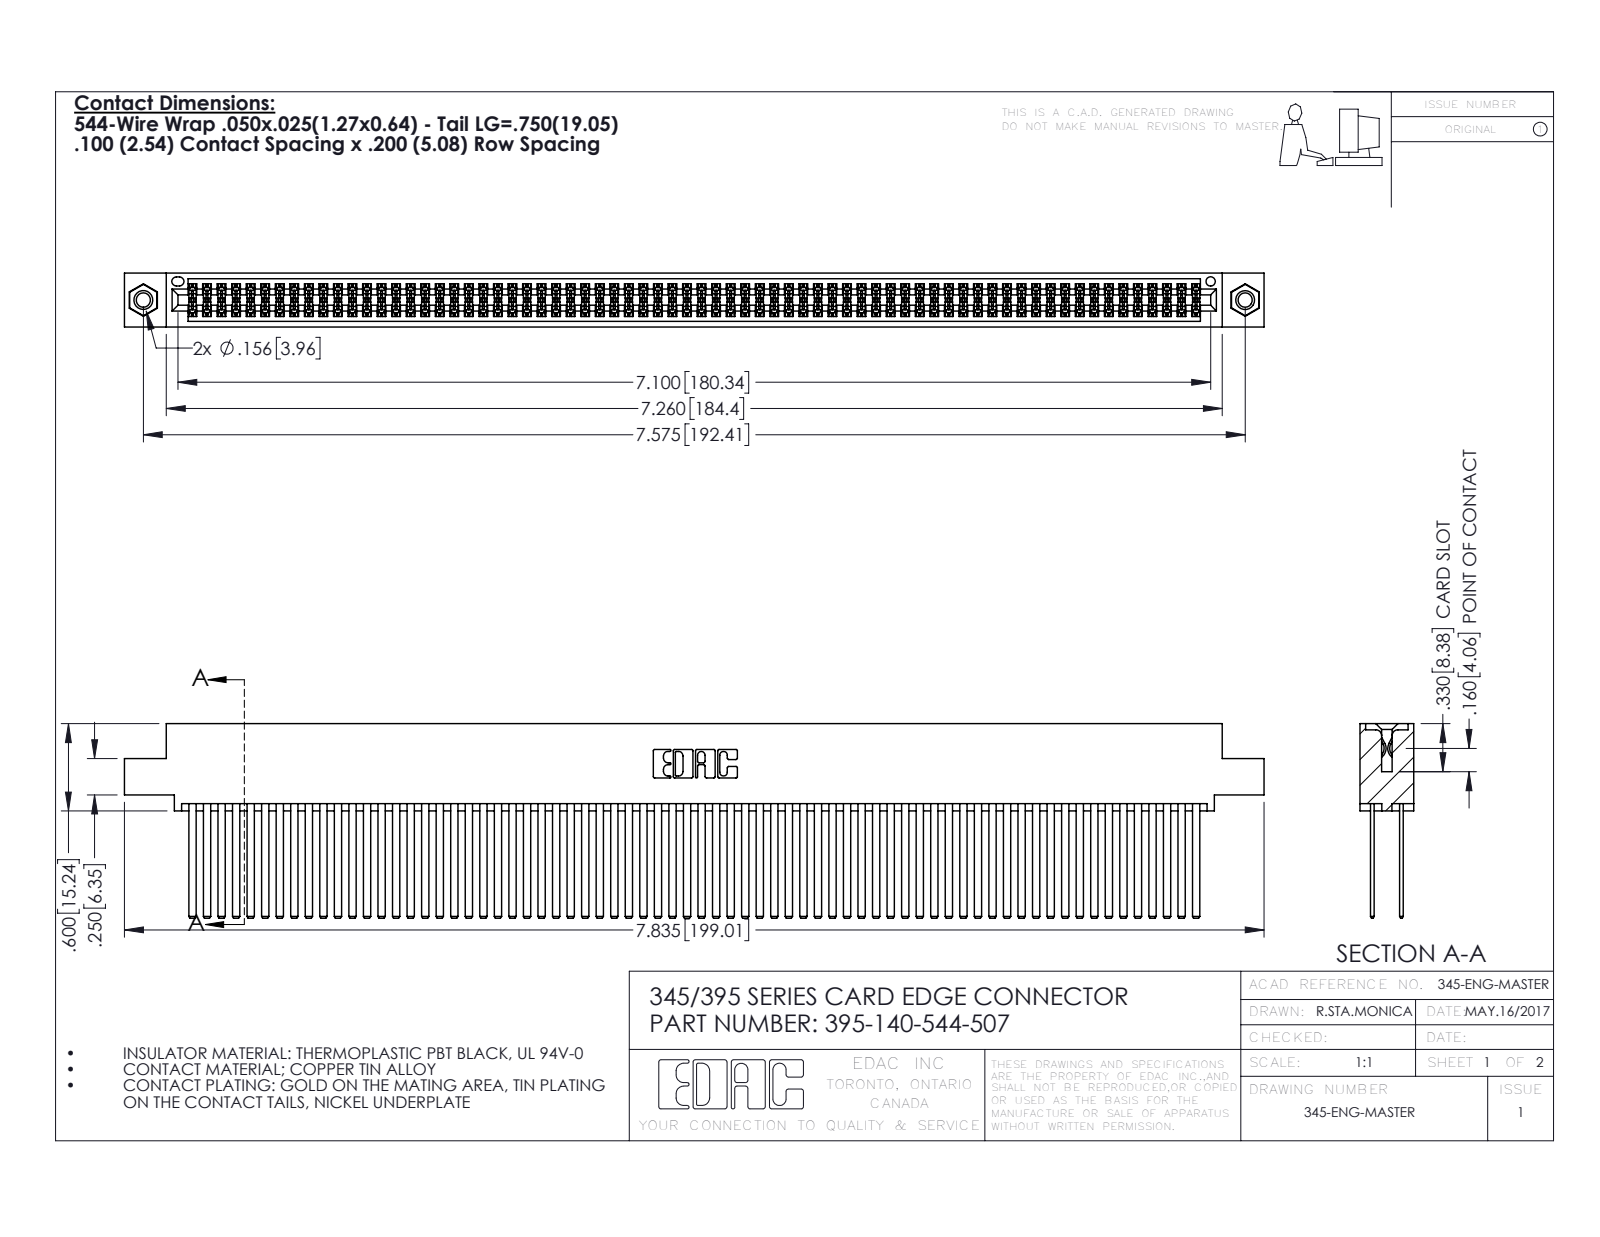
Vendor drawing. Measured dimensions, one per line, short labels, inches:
name: 345-250-001_345-250-005-103; 345 Part_0.110 Offset - 0.156 Dia-TI; 345-292-001_345-293-144; 395-140-544-507
written by: SolidWorks 2016 (CONFIG_CONTROL_DESIGN)
unit: in
bodies: 143 solids, 6350 faces (4176 planar, 2158 cylindrical, 16 other)
size: 7.835 × 1.337 × 0.37
volume: 1.31 in³; area: 59.13 in²
holes: 2× ⌀0.098, 2× ⌀0.125, 2× ⌀0.156, 1× ⌀0.064
bosses: 2× ⌀0.155
rounds: 210× R0.006, 22× R0.01, 6× R0.007, 6× R0.031, 3× R0.026, 2× R0.014, 2× R0.019, 2× R0.022
face distances: 0.2, 0.025, 0.072, 0.098, 0.272, 0.298, 0.225, 0.175, 0.37, 0.149
hole spacings: 0.27, 7.339, 7.575
